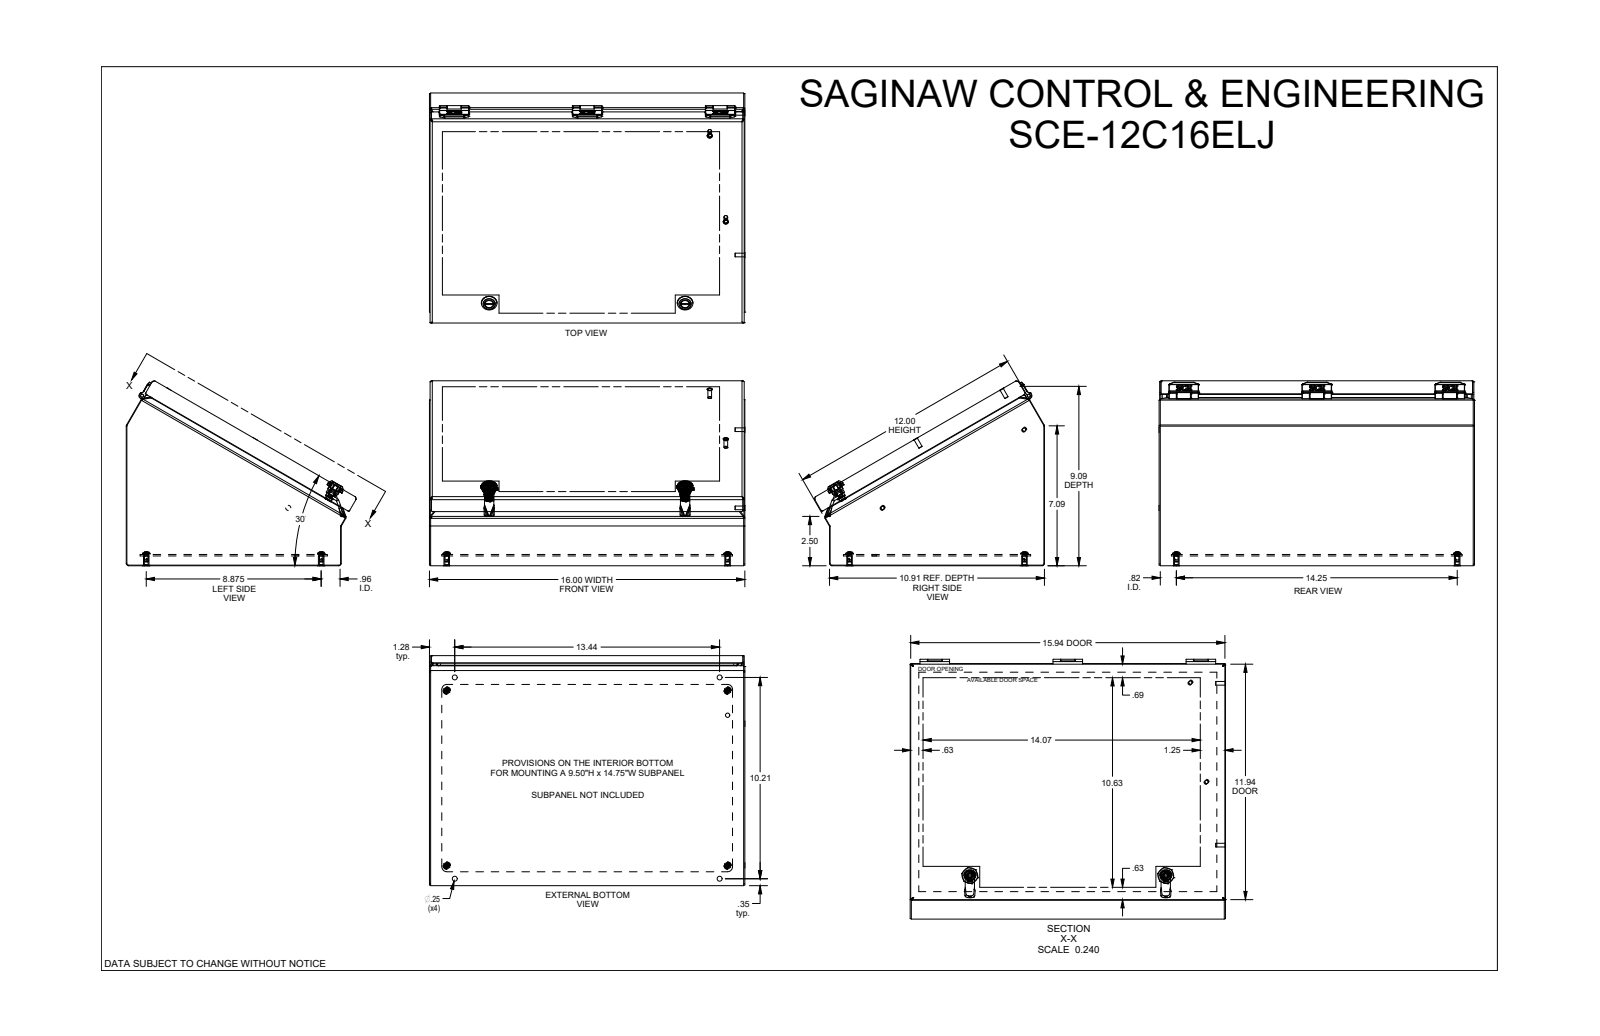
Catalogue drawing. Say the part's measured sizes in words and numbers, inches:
The part is named "SCE-12C16ELJ". Its 3-D file was written by "SolidWorks 2019 (AUTOMOTIVE_DESIGN)". It is 35 solids with 1332 faces: 515 planar, 541 cylindrical and 276 other. Overall it measures 16.004 by 11.665 by 9.38 inches. Its volume is 60.99 cubic inches and its surface area 1 908 square inches. Round holes: 8 of diameter 0.25, 4 of diameter 0.19, 4 of diameter 0.193, 4 of diameter 0.281, 3 of diameter 0.02, 3 of diameter 0.1, 3 of diameter 0.174, 3 of diameter 0.266, 2 of diameter 0.2, 2 of diameter 0.239, 2 of diameter 0.254, 2 of diameter 0.269. Round bosses or shafts: 4 of diameter 0.28, 4 of diameter 0.256, 4 of diameter 0.188, 3 of diameter 0.26, 3 of diameter 0.18, 2 of diameter 0.788, 2 of diameter 0.548, 2 of diameter 0.46. Partial cylindrical surfaces (rounded edges, fillets, slot ends): 36 of radius 0.03, 31 of radius 0.013, 24 of radius 0.06, 22 of radius 0.01, 22 of radius 0.015, 16 of radius 0.12, 13 of radius 0.02, 9 of radius 0.062. The main face-to-face distances are 0.06, 0.06, 0.436, 0.496, 0.075, 0.511, 0.571, 15.94, 15.88, 16. The hole center spacings are 0.78, 6.75, 9.549, 9.94, 13.86, 16.813, 8.875, 10.206.
